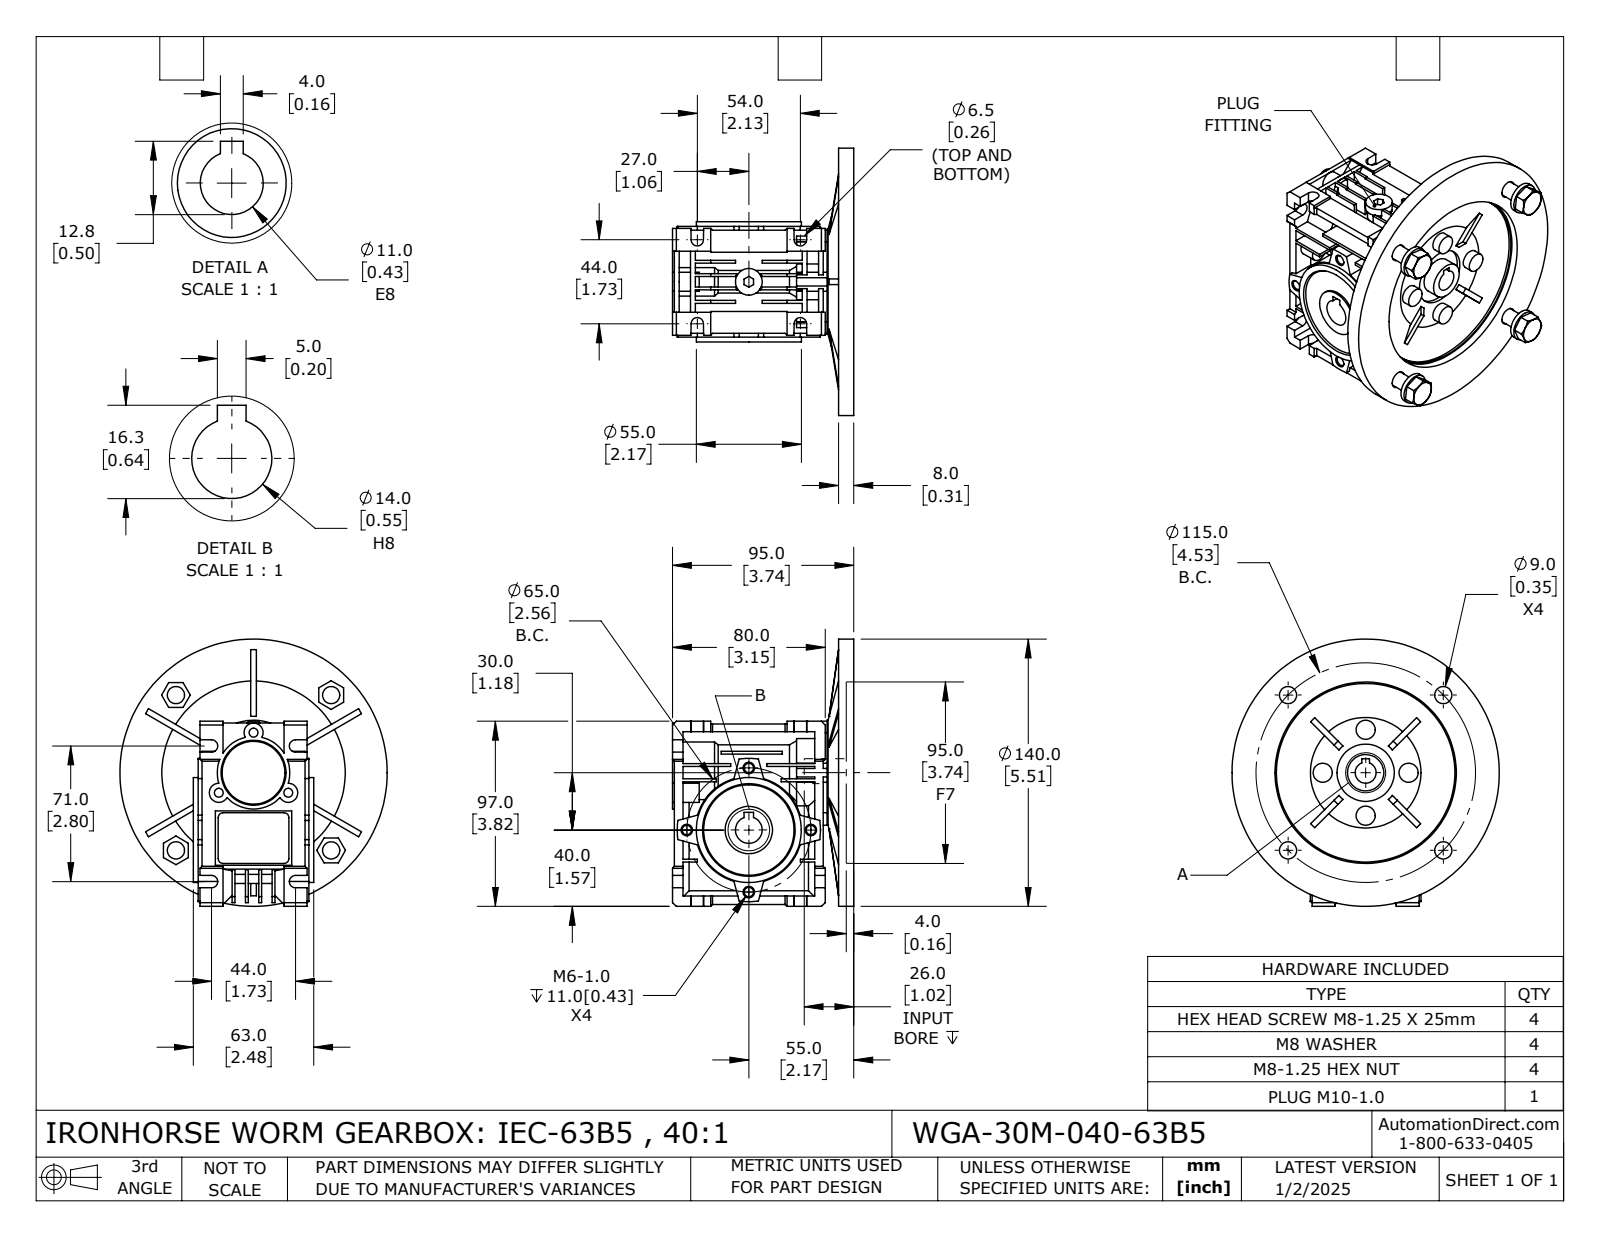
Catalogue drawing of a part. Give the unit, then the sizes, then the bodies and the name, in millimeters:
Units: millimetres
Overall size (bounding box): 140 × 140 × 112.98
Round holes (diameter × count): ⌀9 ×5, ⌀4.92 ×4, ⌀6.8 ×4, ⌀8 ×4, ⌀9.12 ×4, ⌀4.65 ×3, ⌀4.92 ×2, ⌀11 ×1, ⌀11.5 ×1, ⌀14 ×1, ⌀14.5 ×1, ⌀19 ×1
Round bosses / shafts (diameter × count): ⌀16 ×4, ⌀10 ×4, ⌀55 ×2, ⌀140 ×1, ⌀56 ×1, ⌀38 ×1, ⌀37 ×1, ⌀14 ×1
Partial cylindrical surfaces — rounded edges, fillets, slot ends (radius × count): R3.25 ×8, R2.5 ×4, R5 ×3, R7.5 ×1, R17 ×1, R21.5 ×1, R37.5 ×1
Main face-to-face distances: 1.5, 8, 7, 5.5, 1, 14, 4, 4.5, 8.5, 2
Hole centre spacings: 32.5, 45.96, 57.5, 81.32, 21, 36.37, 37.61, 45.16
Volume: 404 435 mm³ · Surface area: 140 309 mm²
Bodies: 18 solids, 1048 faces (618 planar, 256 cylindrical, 174 other)
Part name (STEP PRODUCT): WGA-30M-040-63B5
STEP written by: SolidWorks 2024 (CONFIG_CONTROL_DESIGN)
